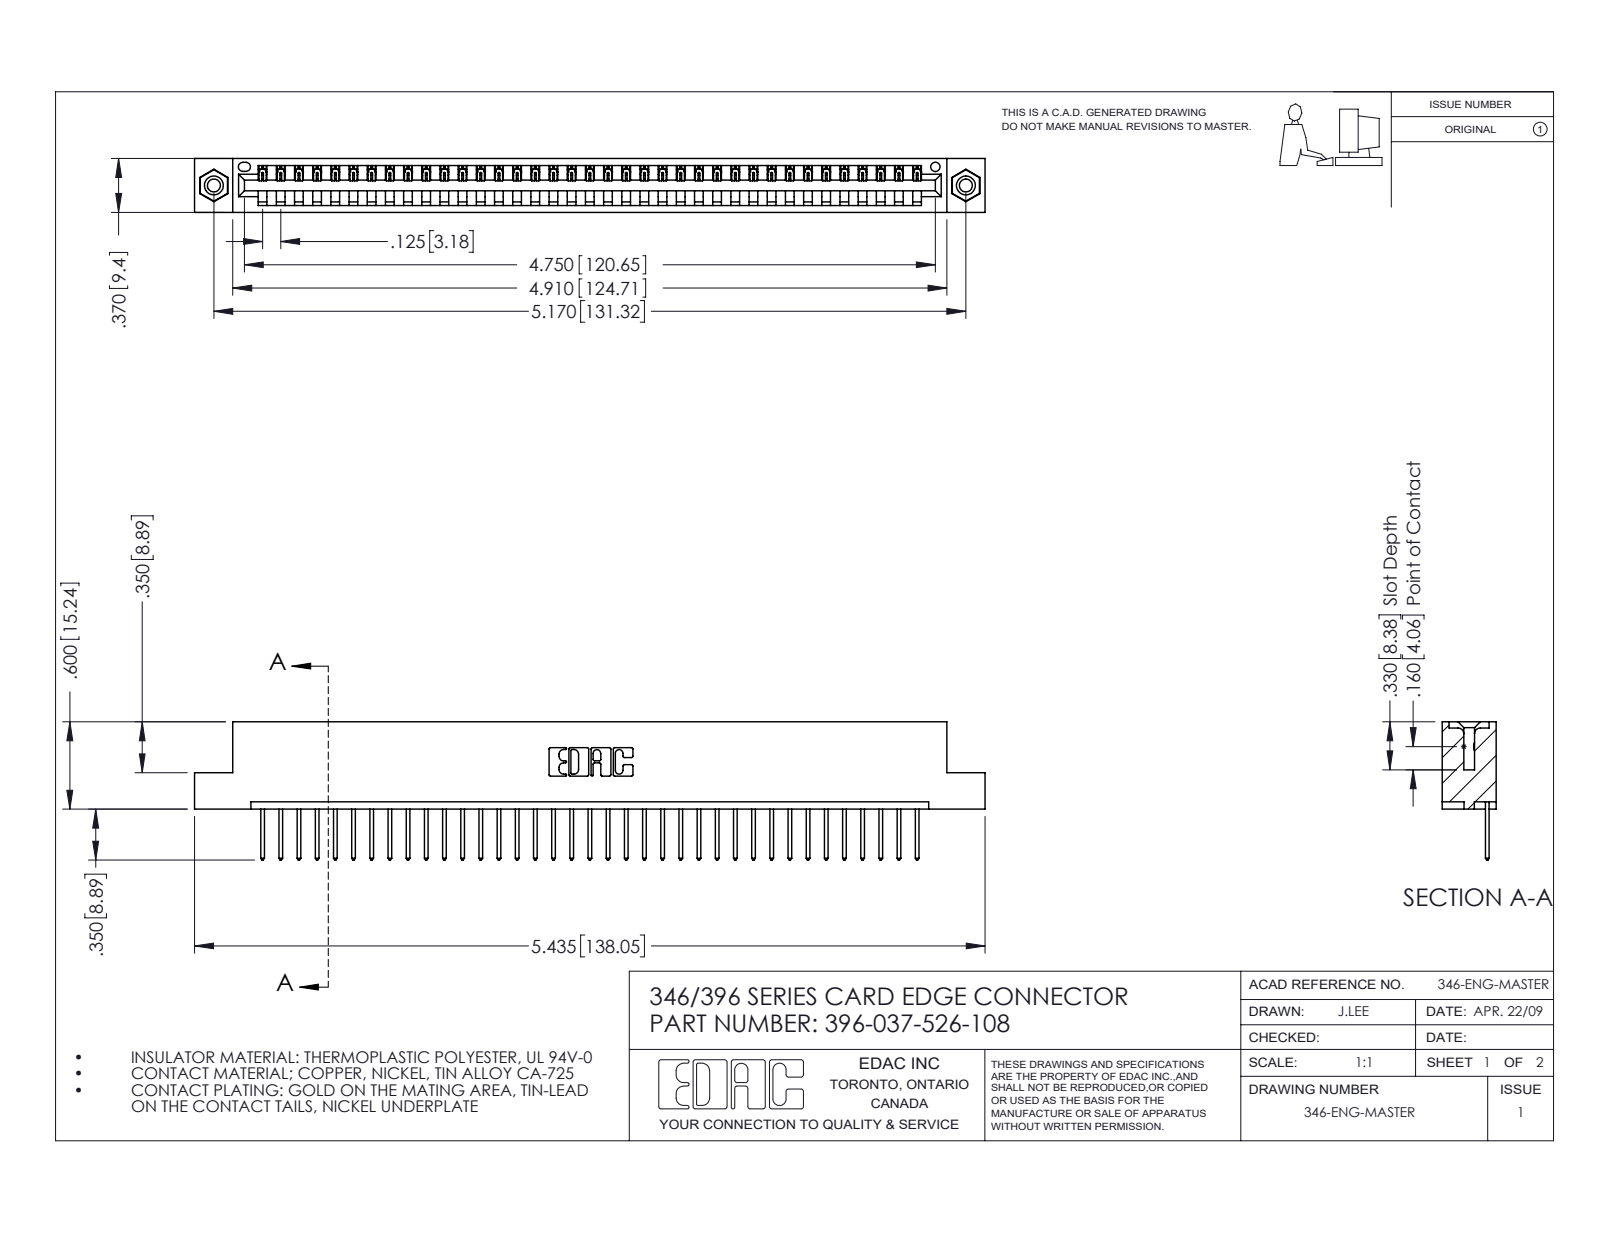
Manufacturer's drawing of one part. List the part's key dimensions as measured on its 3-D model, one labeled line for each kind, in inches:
Part name (STEP PRODUCT): 346 Part_Flush Mounting Lugs - 0.156 Dia-TI; 345-250-001_345-250-003-102; 396-037-526-108; 345-292-001_345-293-126
STEP written by: SolidWorks 2016 (CONFIG_CONTROL_DESIGN)
Units: inches
Bodies: 40 solids, 2328 faces (1588 planar, 724 cylindrical, 16 other)
Overall size (bounding box): 5.435 × 0.95 × 0.37
Volume: 0.802 in³ · Surface area: 25.36 in²
Round holes (diameter × count): ⌀0.089 ×2, ⌀0.125 ×2, ⌀0.156 ×2, ⌀0.064 ×1
Round bosses / shafts (diameter × count): ⌀0.155 ×2
Partial cylindrical surfaces — rounded edges, fillets, slot ends (radius × count): R0.006 ×74, R0.01 ×74, R0.01 ×22, R0.007 ×6, R0.031 ×6, R0.026 ×3, R0.031 ×2, R0.04 ×2
Main face-to-face distances: 0.048, 0.322, 0.37, 0.25, 0.072, 0.298, 0.025, 0.148, 0.222, 0.1
Hole centre spacings: 0.246, 4.961, 5.17
